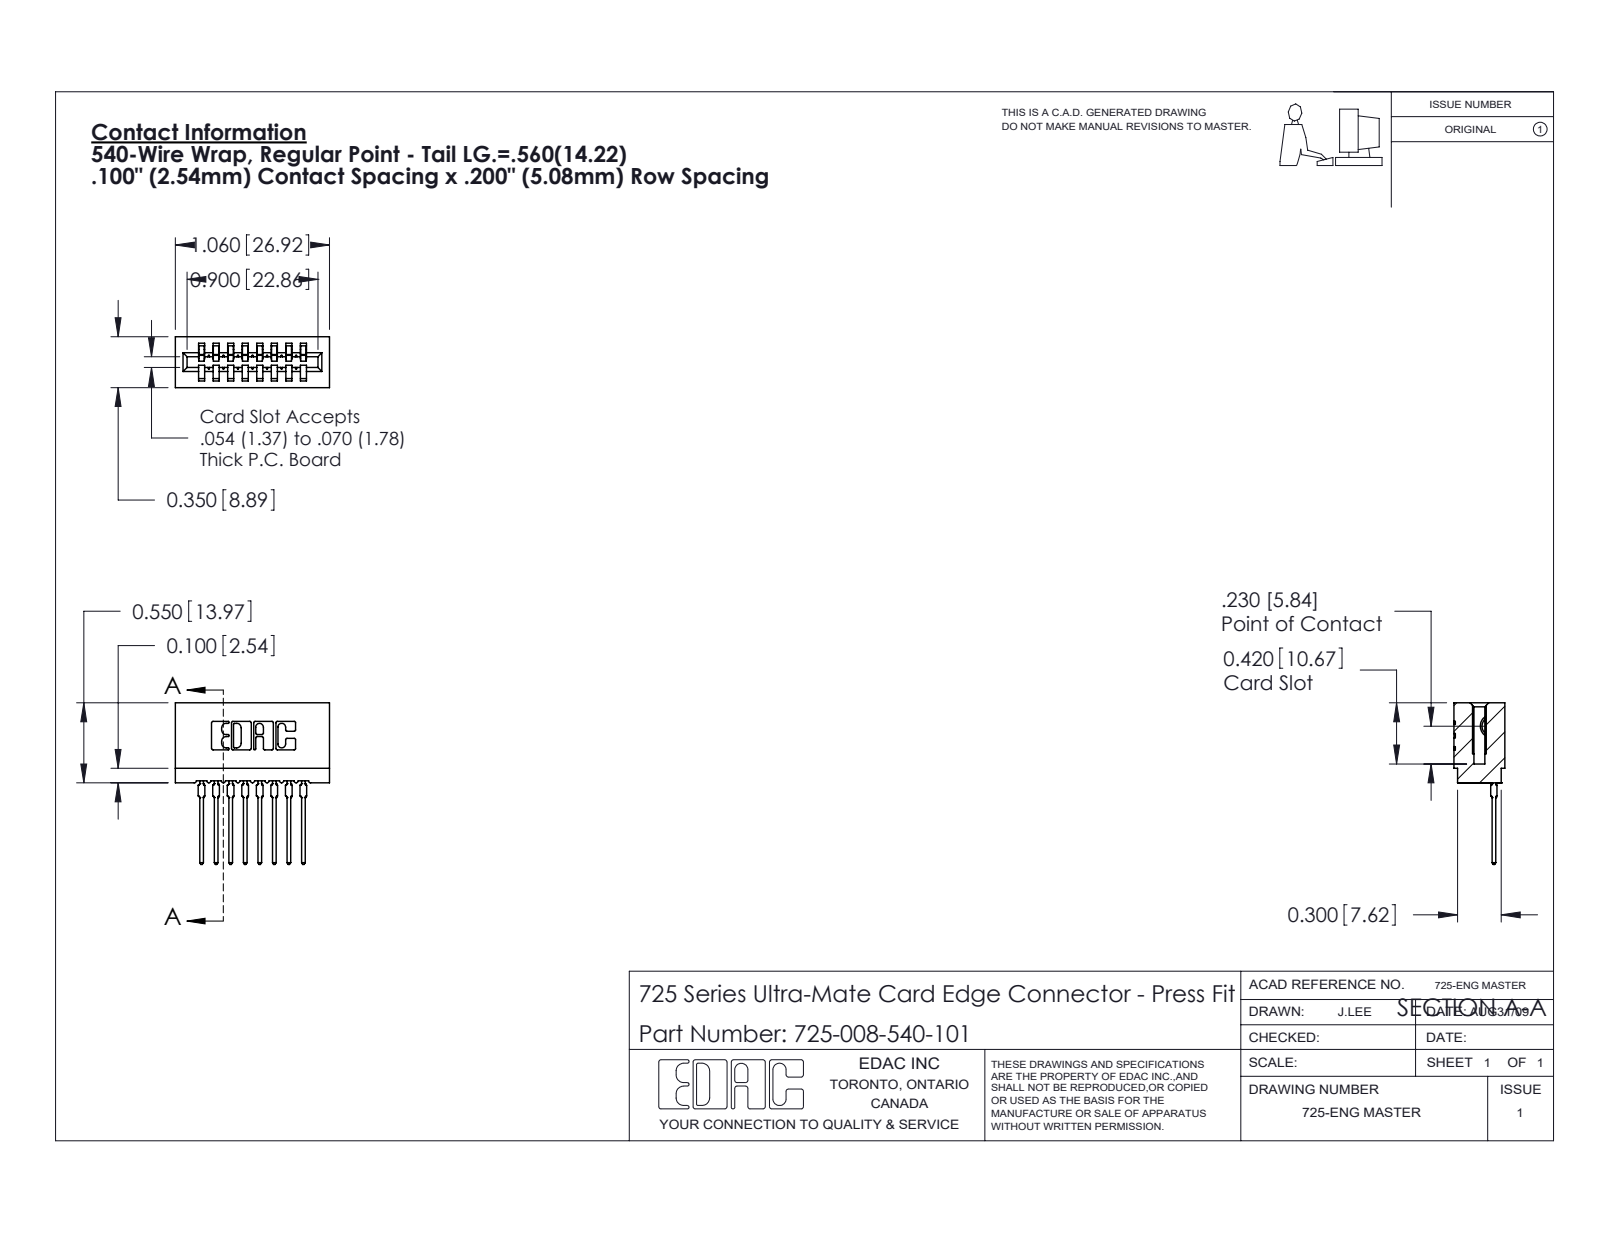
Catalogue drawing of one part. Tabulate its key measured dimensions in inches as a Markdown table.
| quantity | value |
| --- | --- |
| part name | 725-008-540-101; 725 Part_Insulator Option - 01; 745-292-001_540 |
| STEP written by | SolidWorks 2020 (CONFIG_CONTROL_DESIGN) |
| units | inches |
| bodies | 9 solids, 991 faces (591 planar, 192 cylindrical, 208 other) |
| overall size | 1.111 × 1.06 × 0.35 |
| volume | 0.137 in³ |
| surface area | 5.898 in² |
| partial cylindrical surfaces (radius × count) | 0.01 × 22, 0.015 × 16, 0.021 × 16, 0.007 × 6, 0.031 × 6, 0.005 × 4, 0.011 × 4, 0.026 × 3 |
| main face-to-face distances | 0.1, 0.2, 0.3, 0.4, 0.042, 0.142, 0.058, 0.5, 0.242, 0.158 |
